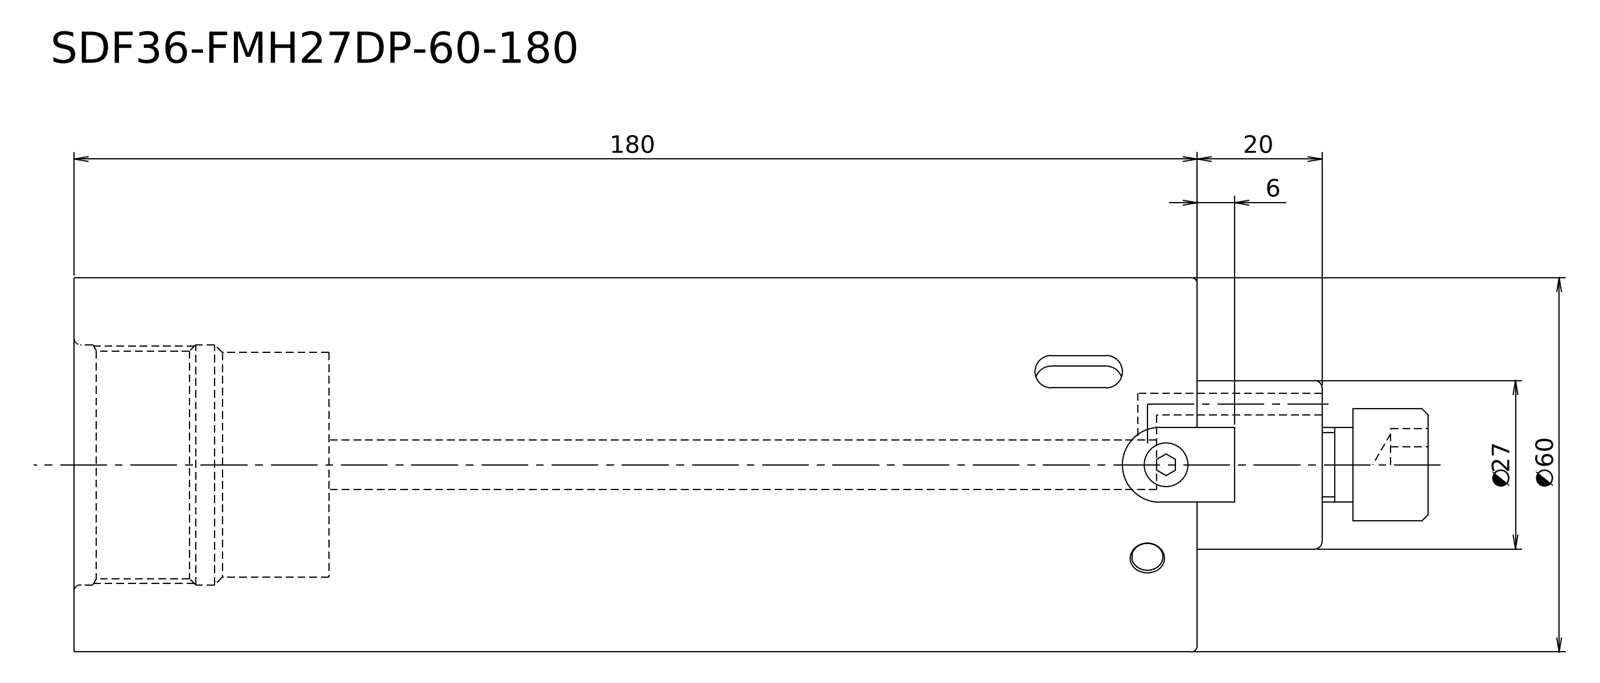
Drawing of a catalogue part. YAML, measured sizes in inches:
step_written_by: "Kubotek KeyCreator V8.5.1 (14335) (CONFIG_CONTROL_DESIGN)"
units: inches
bodies: {solids: 1, faces: 5, planar: 3, cylindrical: 2, other: 0}
overall_size: [7.874, 2.362, 2.362]
volume: 31.76
surface_area: 63.99
round_bosses_or_shafts:
  - {diameter: 2.362, count: 1}
  - {diameter: 1.063, count: 1}
face_to_face_distances: [7.087, 0.787, 7.874]
